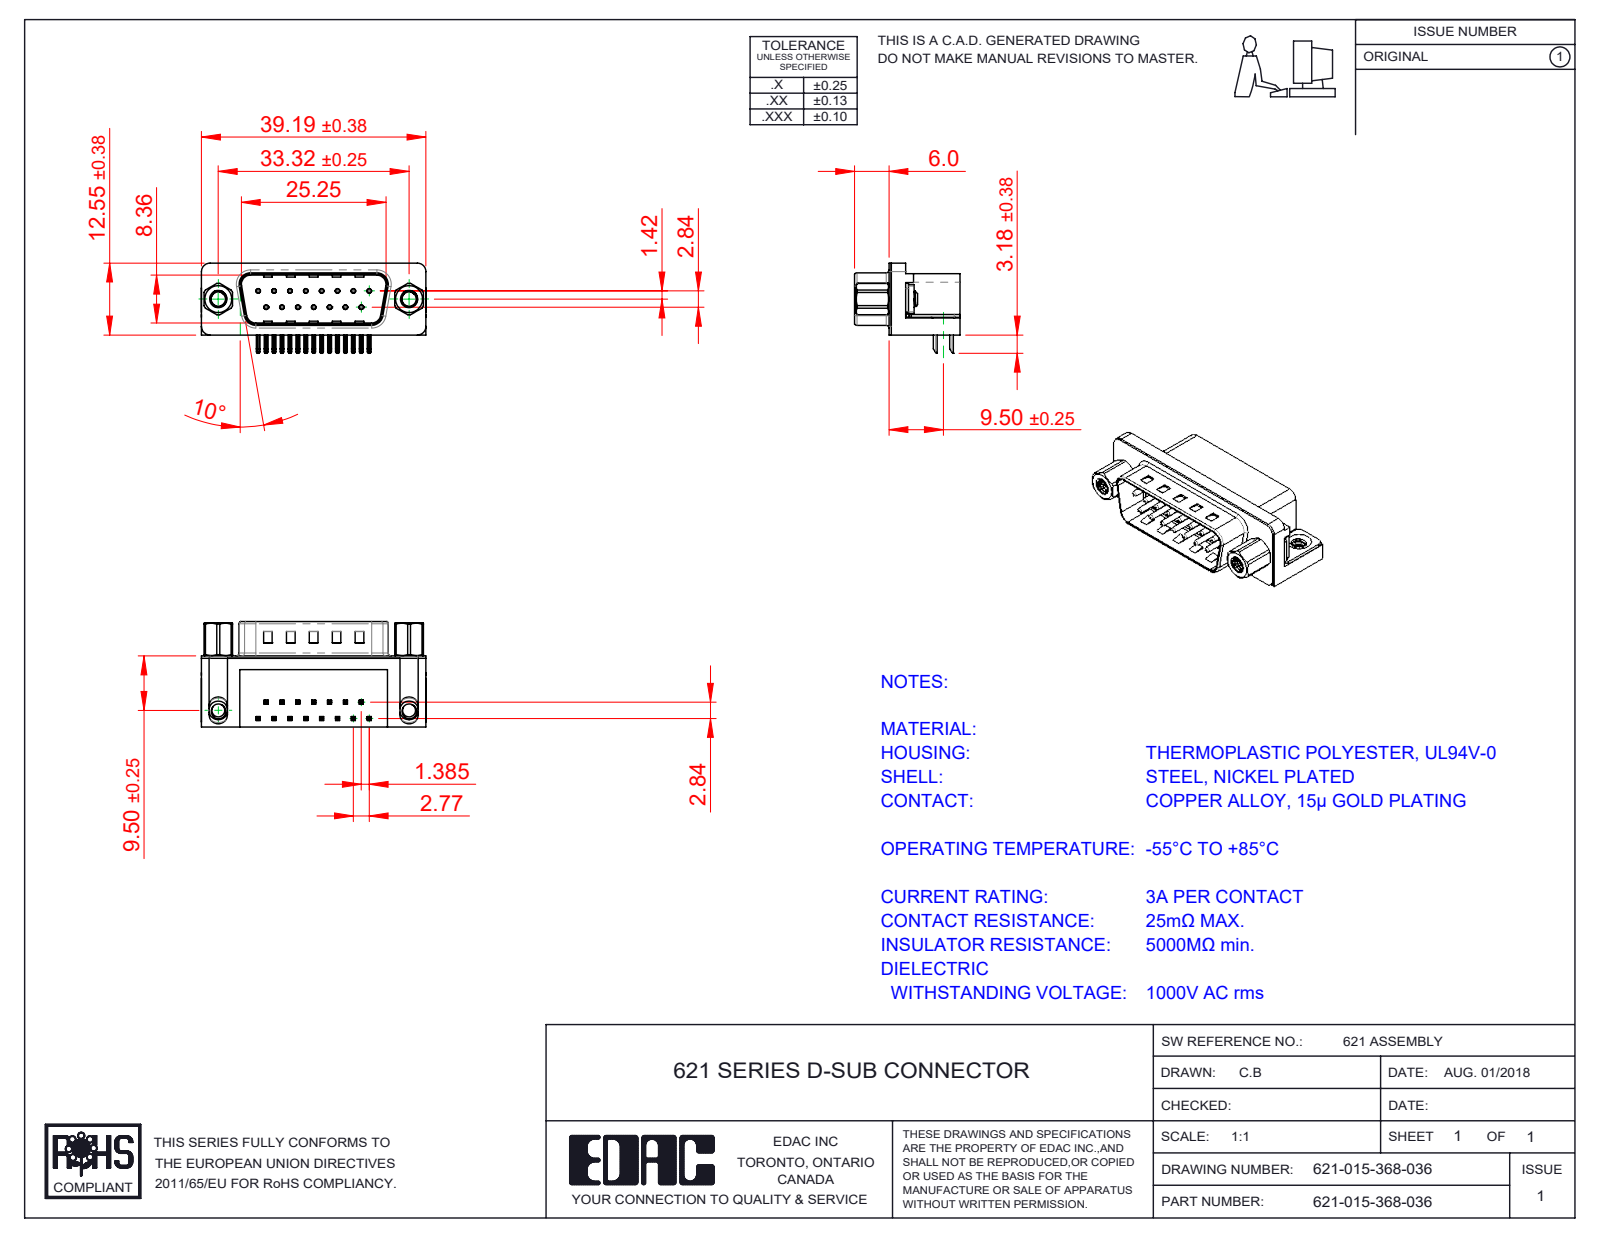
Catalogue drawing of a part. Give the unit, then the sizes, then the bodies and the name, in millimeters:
Units: millimetres
Overall size (bounding box): 39.22 × 18.4 × 16.25
Round holes (diameter × count): ⌀0.35 ×15, ⌀0.8 ×15, ⌀2.5 ×2, ⌀4 ×2, ⌀4.8 ×2, ⌀5 ×2
Round bosses / shafts (diameter × count): ⌀0.75 ×15, ⌀4.9 ×2, ⌀4.75 ×2, ⌀3.9 ×2, ⌀3 ×2
Partial cylindrical surfaces — rounded edges, fillets, slot ends (radius × count): R0.25 ×68, R0.12 ×30, R1 ×16, R0.5 ×14, R1.6 ×8, R1.5 ×6, R0.32 ×4, R0.9 ×4
Main face-to-face distances: 0.4, 12, 10.35, 12.4, 2.1, 10.46, 1.7, 10.86, 8.76, 9.5
Hole centre spacings: 3.16, 2.77, 5.54, 8.31, 11.08, 5.03, 5.04, 7.48
Volume: 4 654 mm³ · Surface area: 6 188 mm²
Bodies: 23 solids, 1665 faces (947 planar, 549 cylindrical, 169 other)
Part name (STEP PRODUCT): 621 Housing_15 Socket; 621 M3 Hex Standoff 5; 621 Contact Top; 621 Shell_15 Socket (+4 more)
STEP written by: SolidWorks 2016 (CONFIG_CONTROL_DESIGN)
